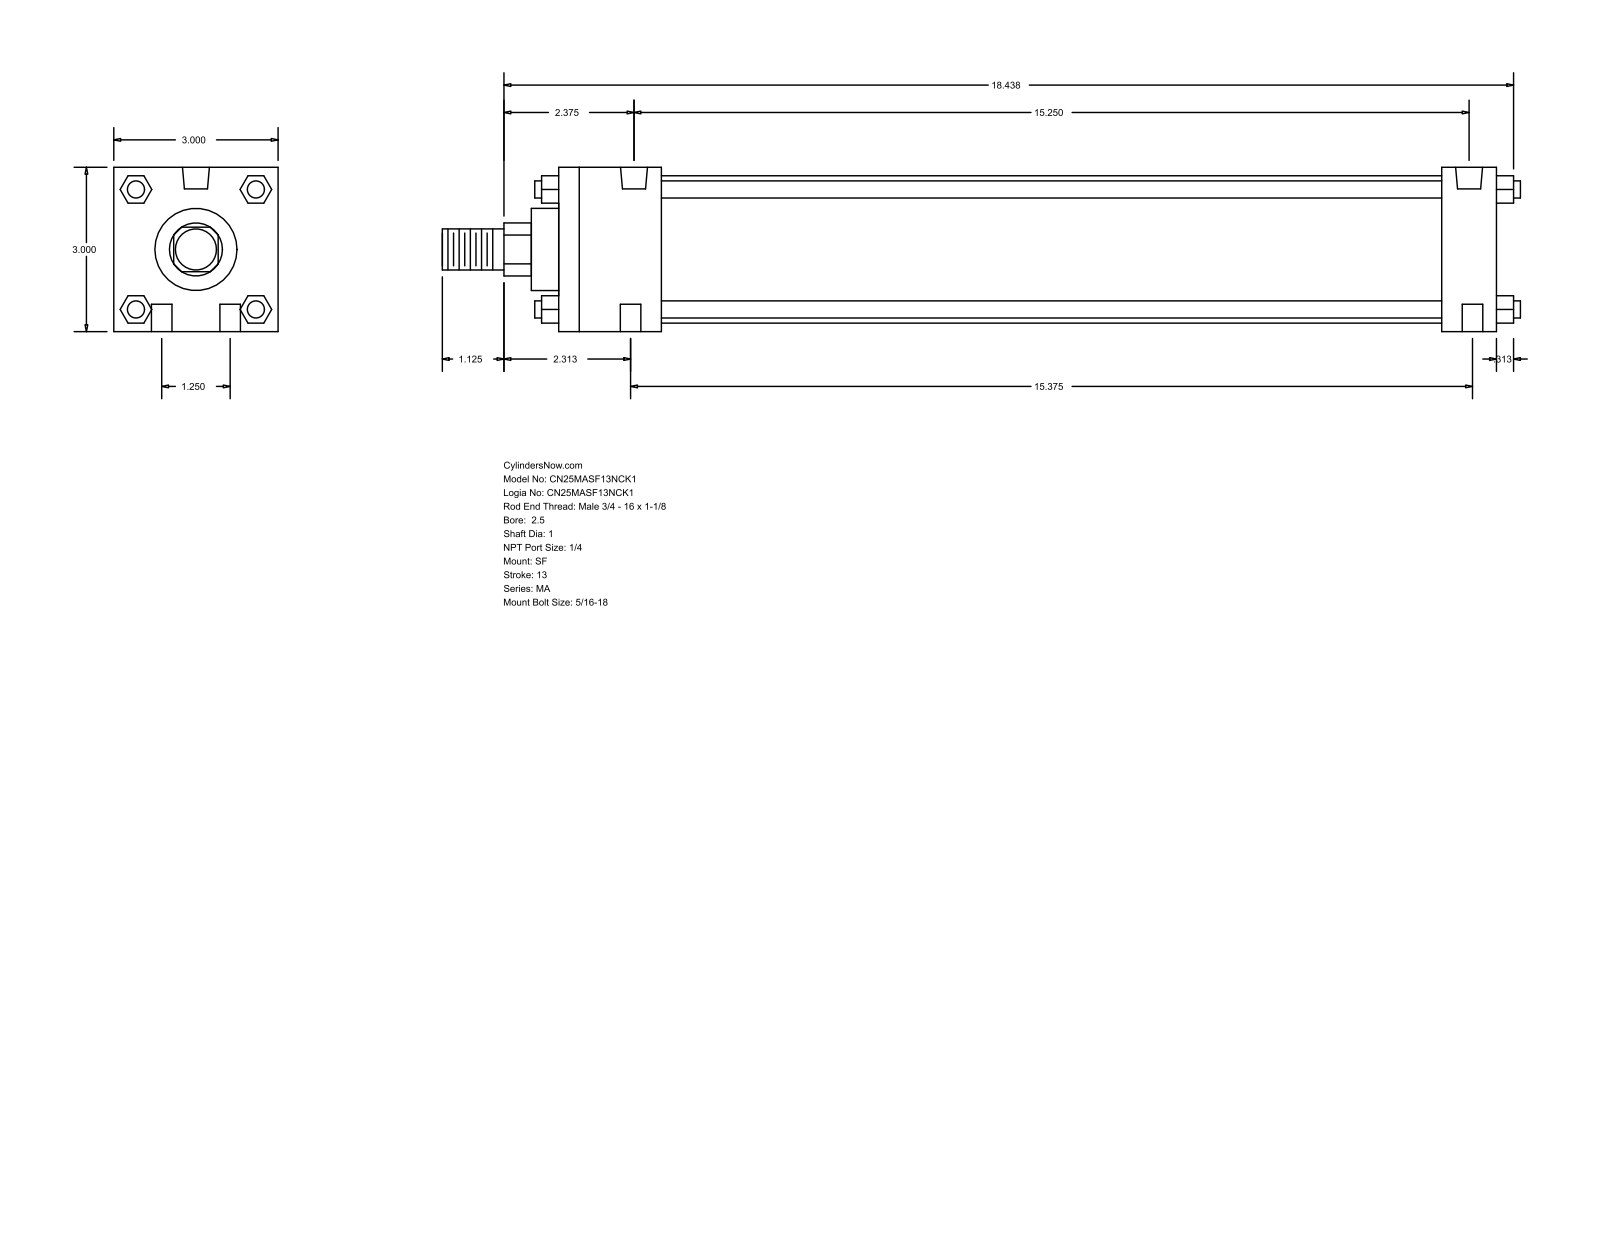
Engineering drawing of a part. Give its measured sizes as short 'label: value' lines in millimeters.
name: MA_SF__0250_1
written by: GSSL Pune (CONFIG_CONTROL_DESIGN)
unit: mm
bodies: 0 solids, 124 faces (94 planar, 30 cylindrical, 0 other)
size: 500.06 × 76.2 × 76.2
holes: 4× ⌀9.53, 2× ⌀7.94, 2× ⌀12.49
bosses: 4× ⌀7.94, 1× ⌀68.33, 1× ⌀38.1, 1× ⌀25.4, 1× ⌀19.05
rounds: 1× R12.29
face distances: 76.2, 434.98, 12.7, 25.4, 409.58, 47.63, 361.95, 387.35, 27.81, 48.17
hole spacings: 15.96, 31.76, 387.35, 389.25, 389.26, 390.52, 391.81
